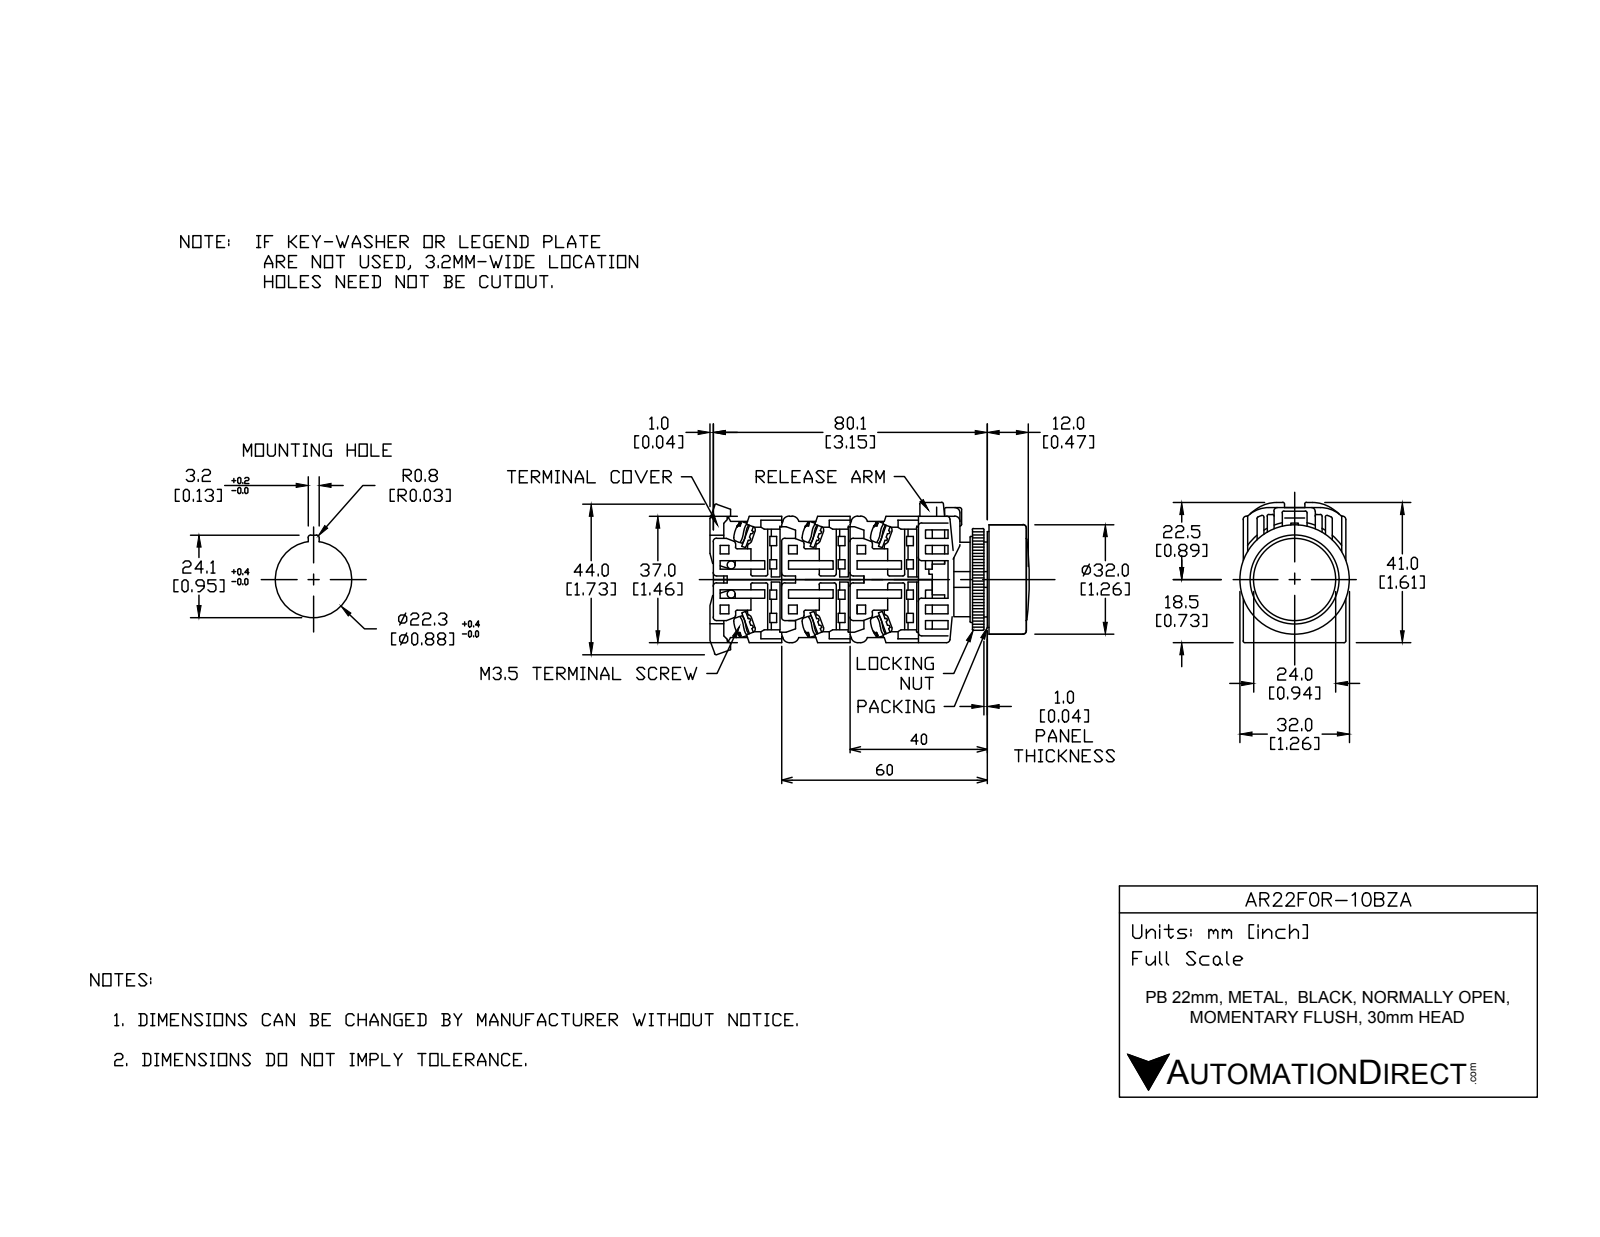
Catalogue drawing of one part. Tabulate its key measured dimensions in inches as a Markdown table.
| quantity | value |
| --- | --- |
| part name | AR22F0R-10BZA |
| STEP written by | SolidWorks 2017 (AUTOMOTIVE_DESIGN) |
| units | inches |
| bodies | 12 solids, 295 faces (201 planar, 74 cylindrical, 20 other) |
| overall size | 2.077 × 1.614 × 1.26 |
| volume | 1.669 in³ |
| surface area | 30.06 in² |
| round holes (diameter × count) | 0.858 × 1, 0.866 × 1, 0.984 × 1, 1.22 × 1 |
| round bosses / shafts (diameter × count) | 0.197 × 2, 1.26 × 1, 1.201 × 1, 1.173 × 1, 0.945 × 1, 0.937 × 1, 0.856 × 1, 0.669 × 1 |
| partial cylindrical surfaces (radius × count) | 0.02 × 23, 0.069 × 4, 0.197 × 4, 0.157 × 2, 0.653 × 1, 0.693 × 1 |
| main face-to-face distances | 0.039, 1.122, 0.709, 0.118, 0.079, 1.142, 1.181, 0.413, 0.315, 0.807 |
